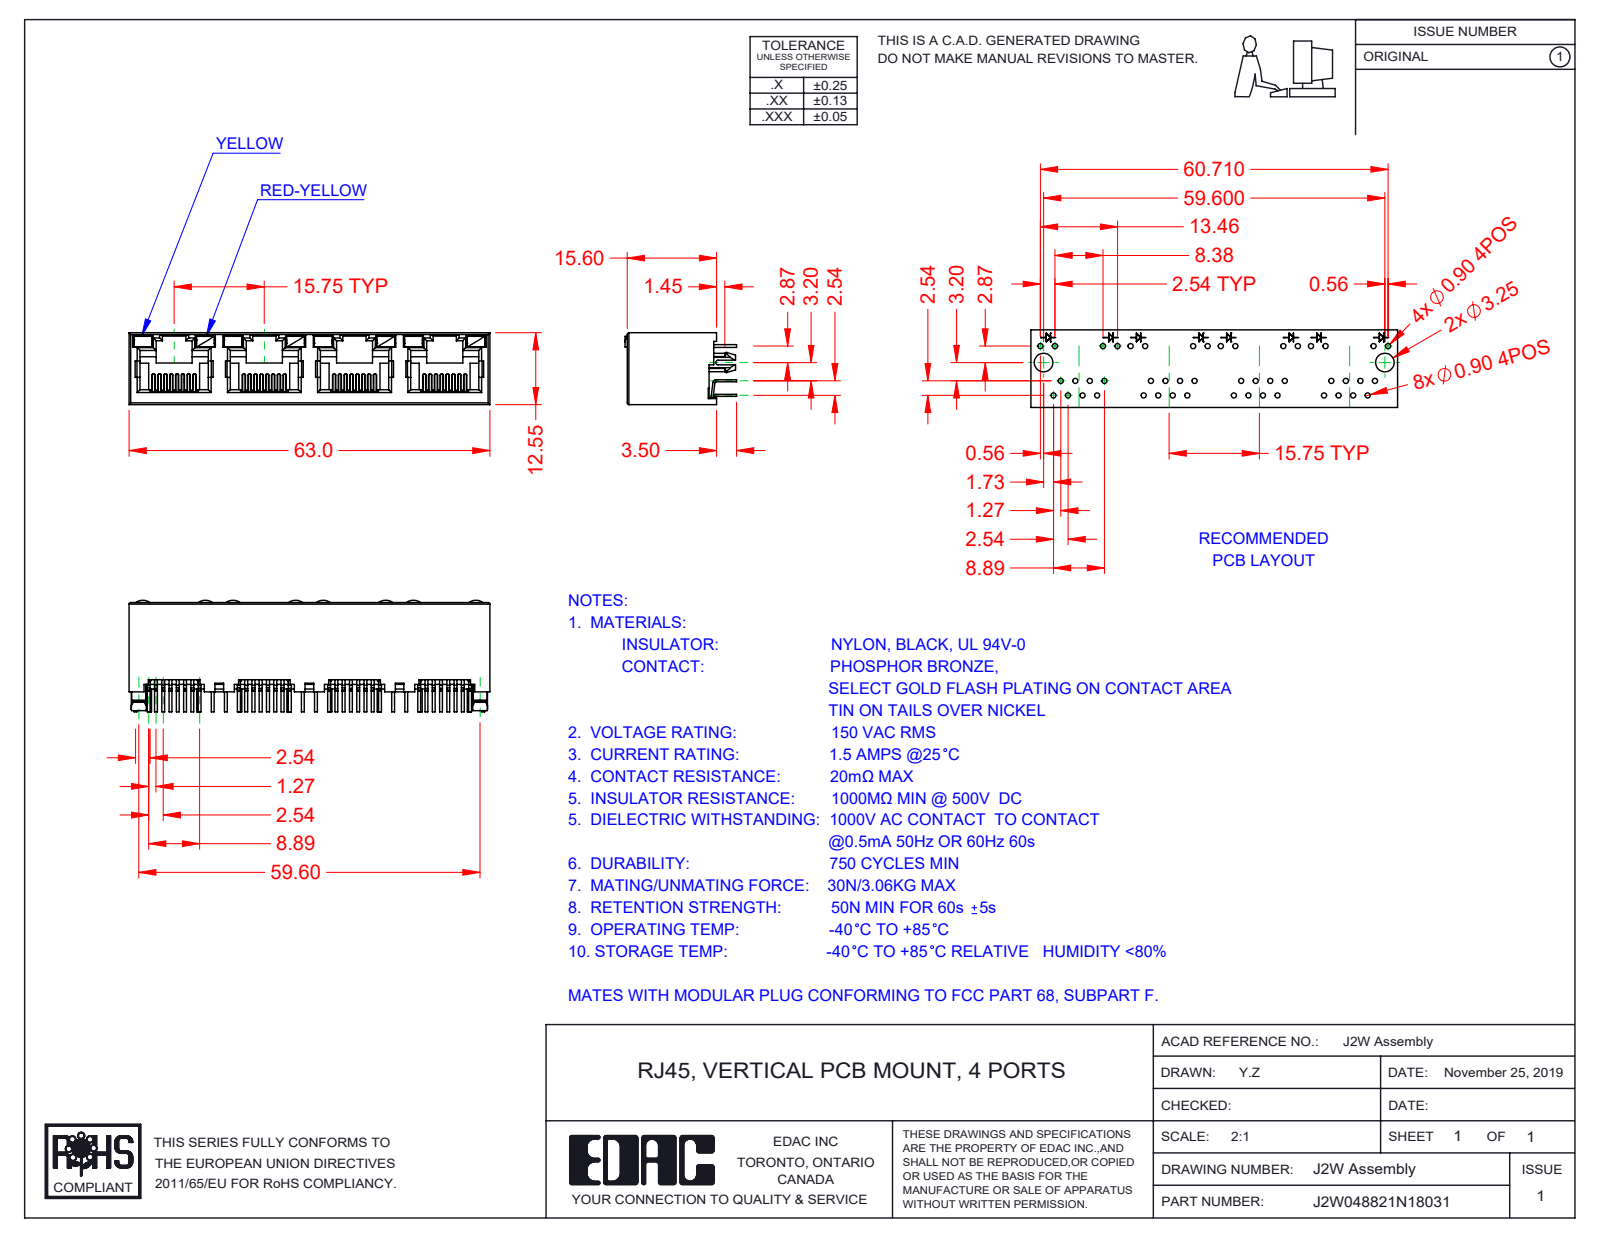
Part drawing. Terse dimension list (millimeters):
name: 2W LED RH_8-Red-Yellow; 2W Contacts; J2W048821N18031; 2W Insulator (+2 more)
written by: SolidWorks 2020 (CONFIG_CONTROL_DESIGN)
unit: mm
bodies: 45 solids, 3139 faces (2600 planar, 481 cylindrical, 58 other)
size: 63 × 19.5 × 12.55
volume: 5 335 mm³; area: 13 144 mm²
rounds: 64× R0.15, 29× R0.2, 28× R0.5, 14× R0.3, 8× R0.45, 8× R2, 2× R0.25, 2× R1.5
face distances: 12.55, 11.9, 0.65, 15.75, 0.36, 1.5, 0.78, 0.6, 11.3, 31.5
